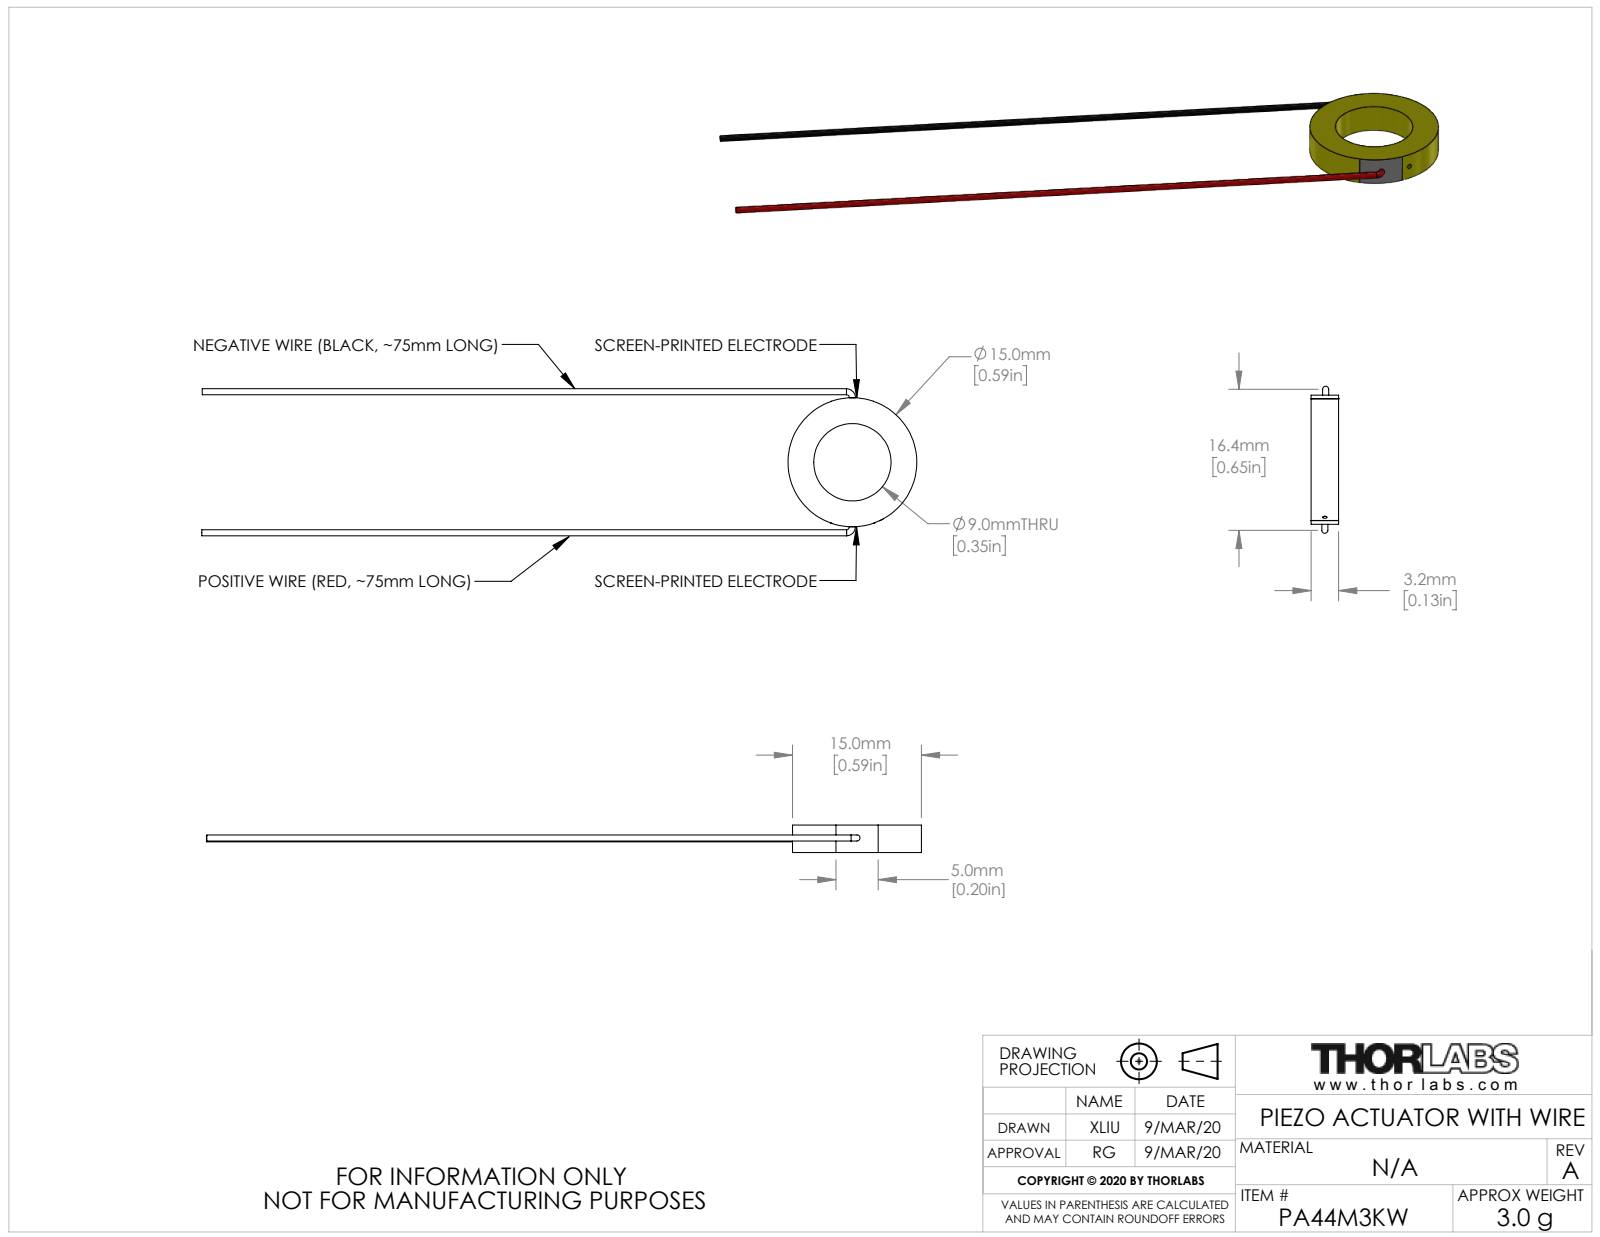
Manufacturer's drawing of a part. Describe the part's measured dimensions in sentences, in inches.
The part is named "CTN015330". Its 3-D file was written by "SolidWorks 2018 (AUTOMOTIVE_DESIGN)". It is 3 solids with 28 faces: 9 planar, 12 cylindrical and 7 other. Overall it measures 3.277 by 0.674 by 0.126 inches. Its volume is 0.026 cubic inches and its surface area 1.25 square inches. Round holes: 1 of diameter 0.354. Round bosses or shafts: 2 of diameter 0.028. Partial cylindrical surfaces (rounded edges, fillets, slot ends): 1 of radius 0.295, 1 of radius 0.296. The main face-to-face distances are 0.126, 0.591.
